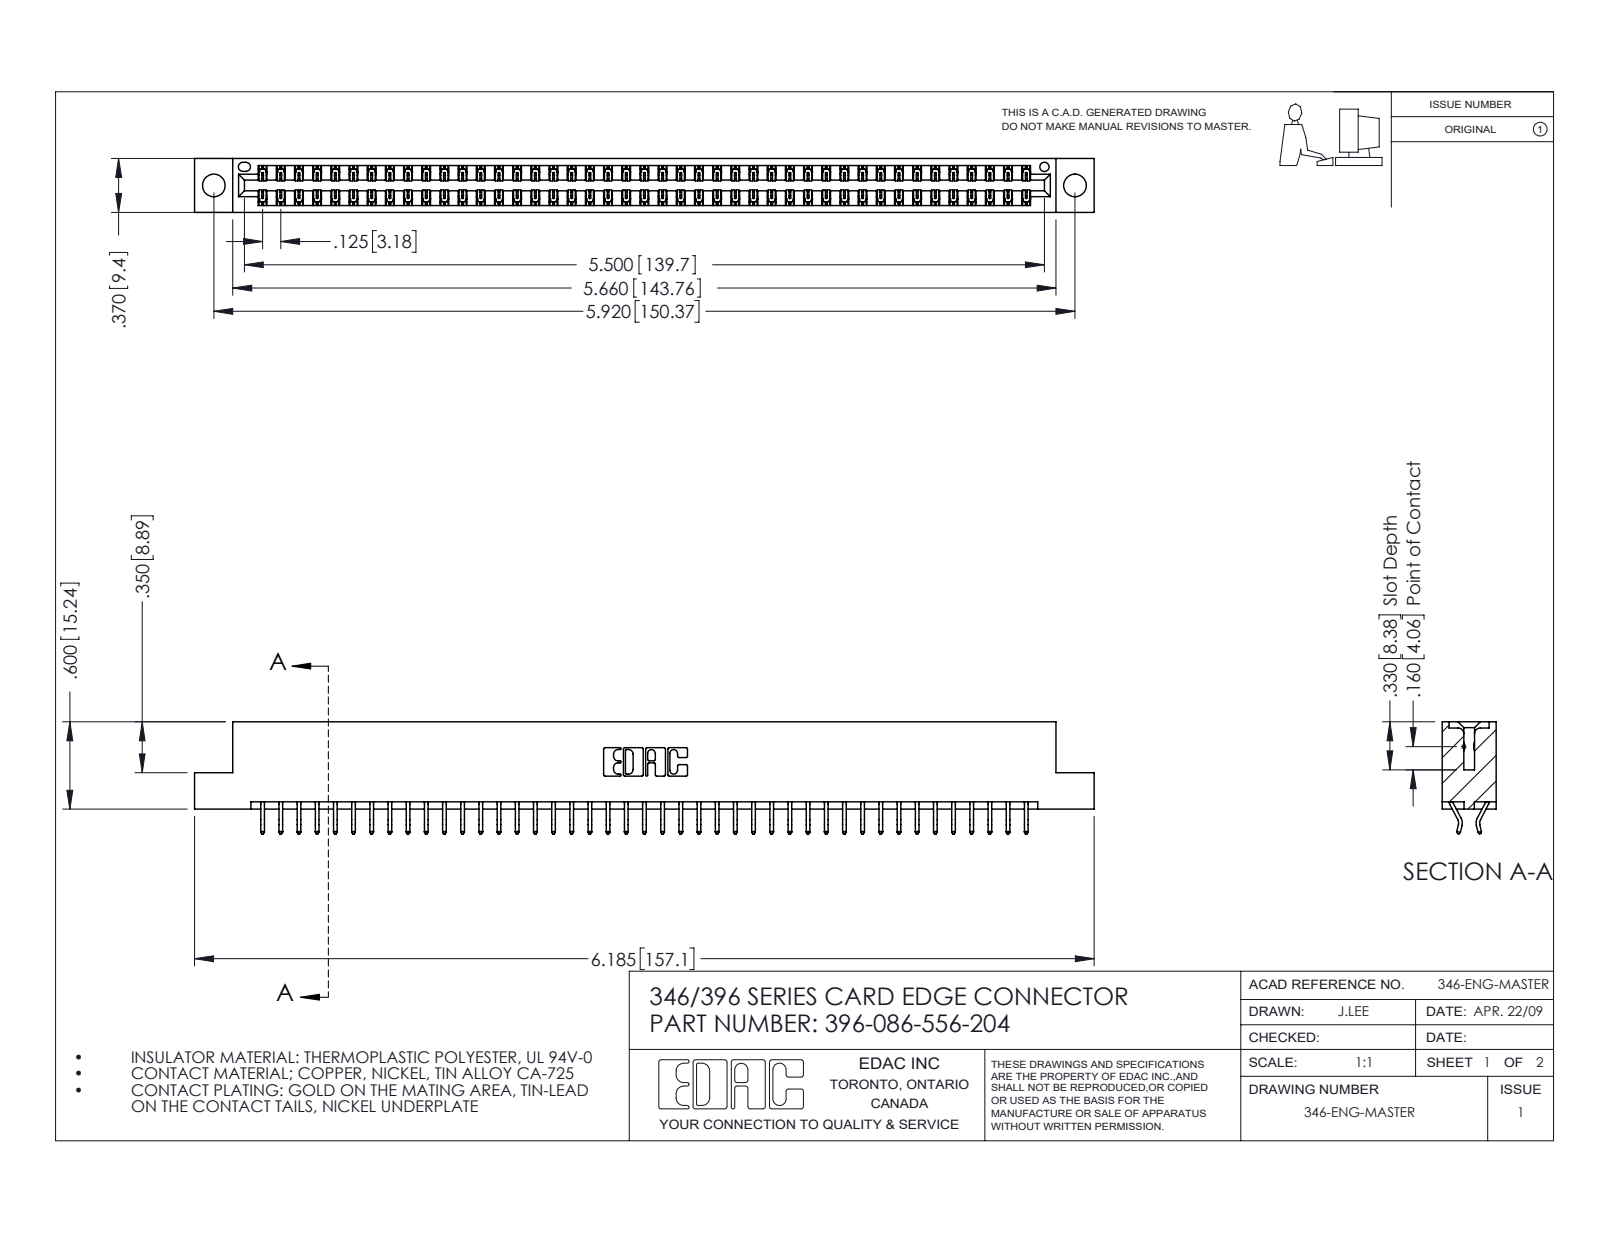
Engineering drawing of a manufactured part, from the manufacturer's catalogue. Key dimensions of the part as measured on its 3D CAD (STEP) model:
Part name (STEP PRODUCT): 346 Part_Flush Mounting Lugs - 0.156 Dia-TH; 396-086-556-204; 345-292-001_556 Tail
STEP written by: SolidWorks 2016 (CONFIG_CONTROL_DESIGN)
Units: inches
Bodies: 87 solids, 5110 faces (3430 planar, 1680 cylindrical, 0 other)
Overall size (bounding box): 6.185 × 0.77 × 0.37
Volume: 0.93 in³ · Surface area: 32.07 in²
Round holes (diameter × count): ⌀0.156 ×2, ⌀0.064 ×1
Partial cylindrical surfaces — rounded edges, fillets, slot ends (radius × count): R0.006 ×129, R0.01 ×22, R0.007 ×6, R0.031 ×6, R0.026 ×3, R0.01 ×2, R0.014 ×2, R0.022 ×2
Main face-to-face distances: 0.048, 0.322, 0.37, 0.25, 0.025, 0.072, 0.298, 0.275, 0.148, 0.222
Hole centre spacings: 0.246, 5.711, 5.92
